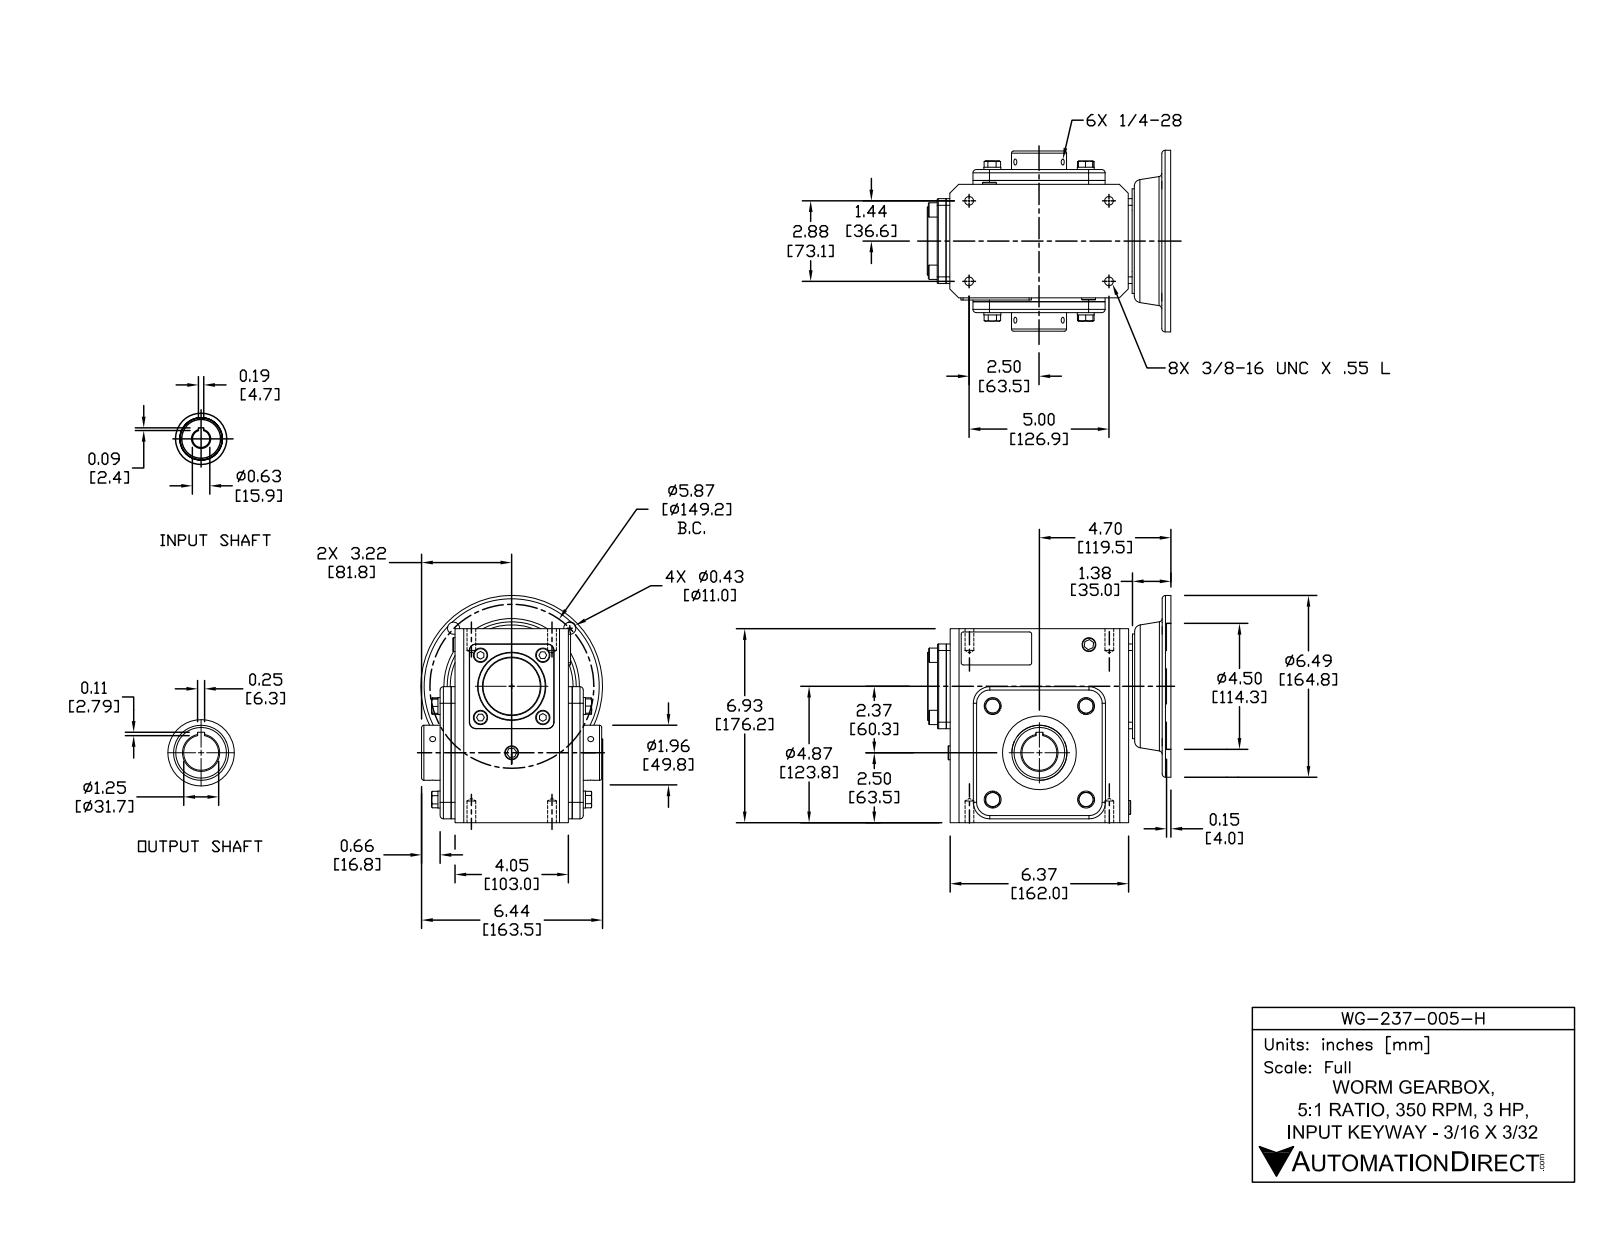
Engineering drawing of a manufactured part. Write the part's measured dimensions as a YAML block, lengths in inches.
part_name: "WG-237-005-H"
step_written_by: "SolidWorks 2015 (CONFIG_CONTROL_DESIGN)"
units: inches
bodies: {solids: 37, faces: 609, planar: 348, cylindrical: 172, other: 89}
overall_size: [8.701, 8.123, 6.496]
volume: 217.1
surface_area: 540.6
round_holes:
  - {diameter: 0.213, count: 6}
  - {diameter: 0.313, count: 4}
  - {diameter: 0.406, count: 4}
  - {diameter: 0.591, count: 1}
  - {diameter: 0.625, count: 1}
  - {diameter: 1.181, count: 1}
  - {diameter: 1.25, count: 1}
  - {diameter: 1.457, count: 1}
  - {diameter: 1.969, count: 1}
  - {diameter: 2.638, count: 1}
  - {diameter: 3.819, count: 1}
  - {diameter: 4.5, count: 1}
round_bosses_or_shafts:
  - {diameter: 0.606, count: 4}
  - {diameter: 0.512, count: 4}
  - {diameter: 6.496, count: 1}
  - {diameter: 3.74, count: 1}
  - {diameter: 2.441, count: 1}
  - {diameter: 2.047, count: 1}
  - {diameter: 1.142, count: 1}
partial_cylinders:
  - {radius: 0.079, count: 8}
  - {radius: 0.118, count: 8}
  - {radius: 0.236, count: 6}
  - {radius: 0.591, count: 4}
  - {radius: 0.02, count: 2}
  - {radius: 0.039, count: 2}
face_to_face_distances: [0.138, 4.331, 4.724, 0.531, 0.394, 4.193, 4.587, 6.516, 0.315, 6.937]
hole_center_spacings: [2.859, 2.937, 4.945, 5.653, 2.098, 2.88, 4.154, 4.154]
